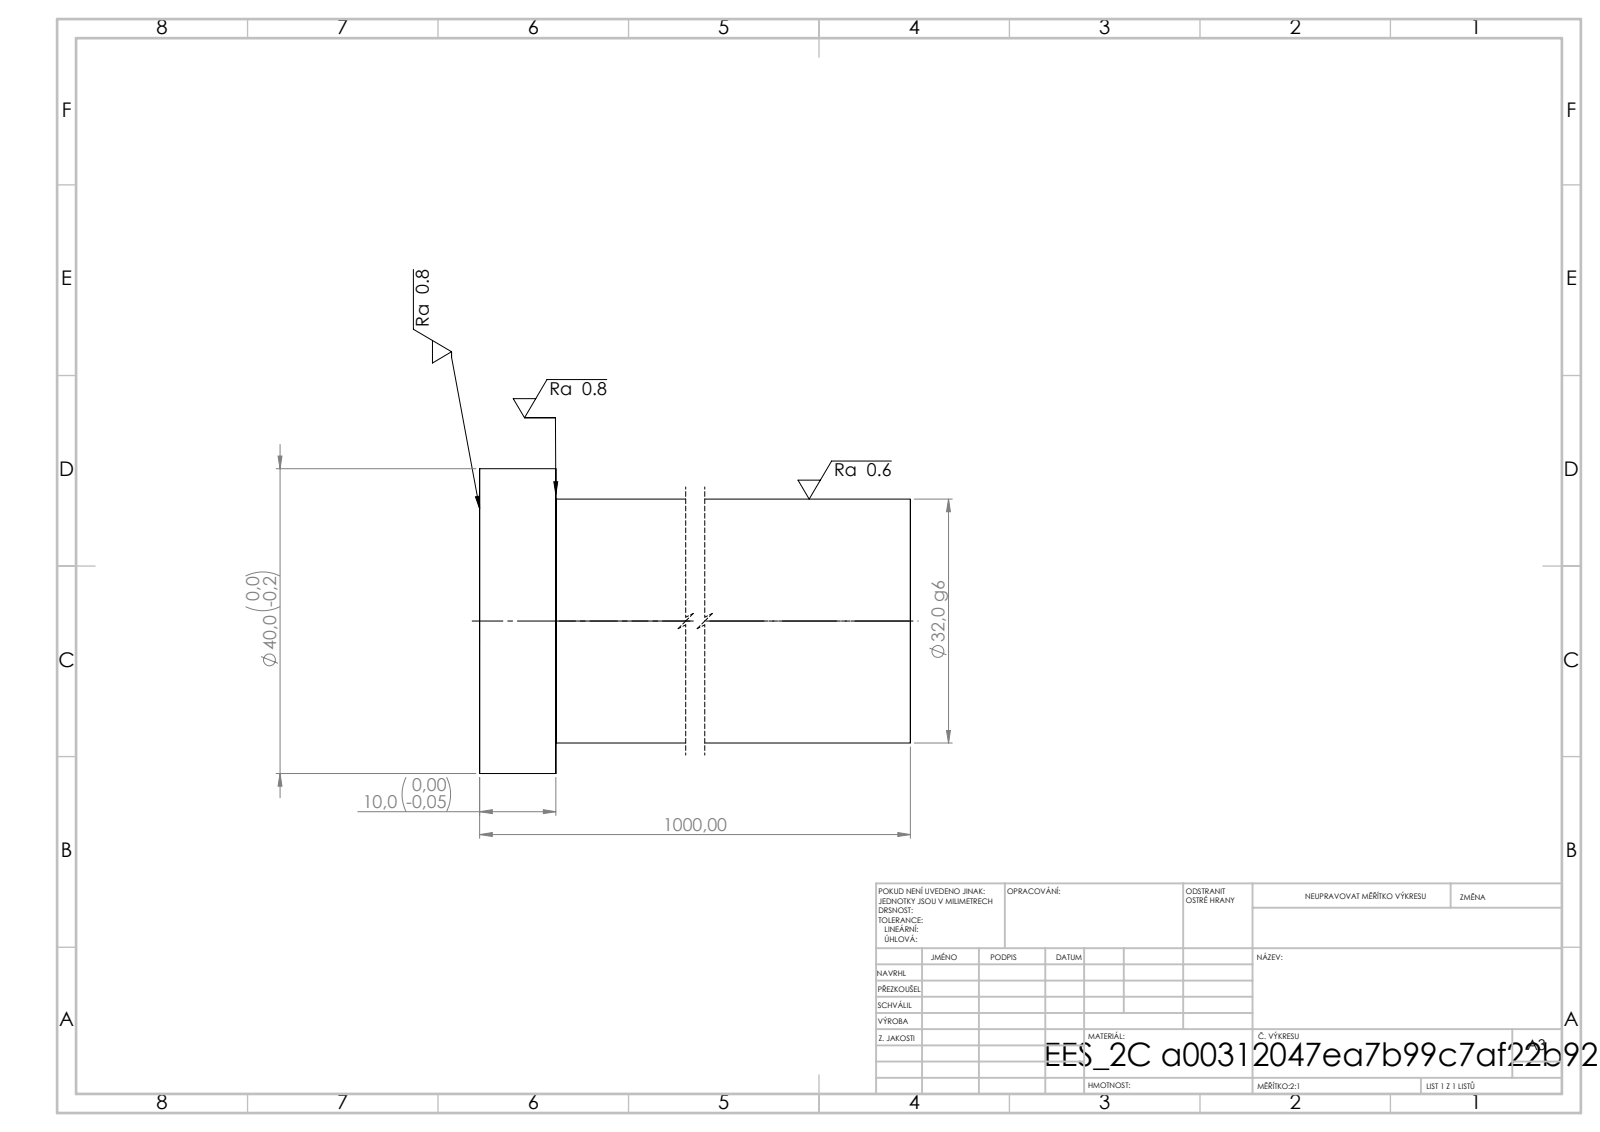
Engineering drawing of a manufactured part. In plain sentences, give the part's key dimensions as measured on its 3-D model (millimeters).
Its 3-D file was written by "SolidWorks 2019 (CONFIG_CONTROL_DESIGN)". It is 1 solid with 7 faces: 3 planar, 4 cylindrical and 0 other. Overall it measures 1000 by 40 by 40 millimeters. Its volume is 808 772 cubic millimeters and its surface area 103 296 square millimeters. Round bosses or shafts: 1 of diameter 40, 1 of diameter 32. The main face-to-face distances are 1000, 10, 990.
